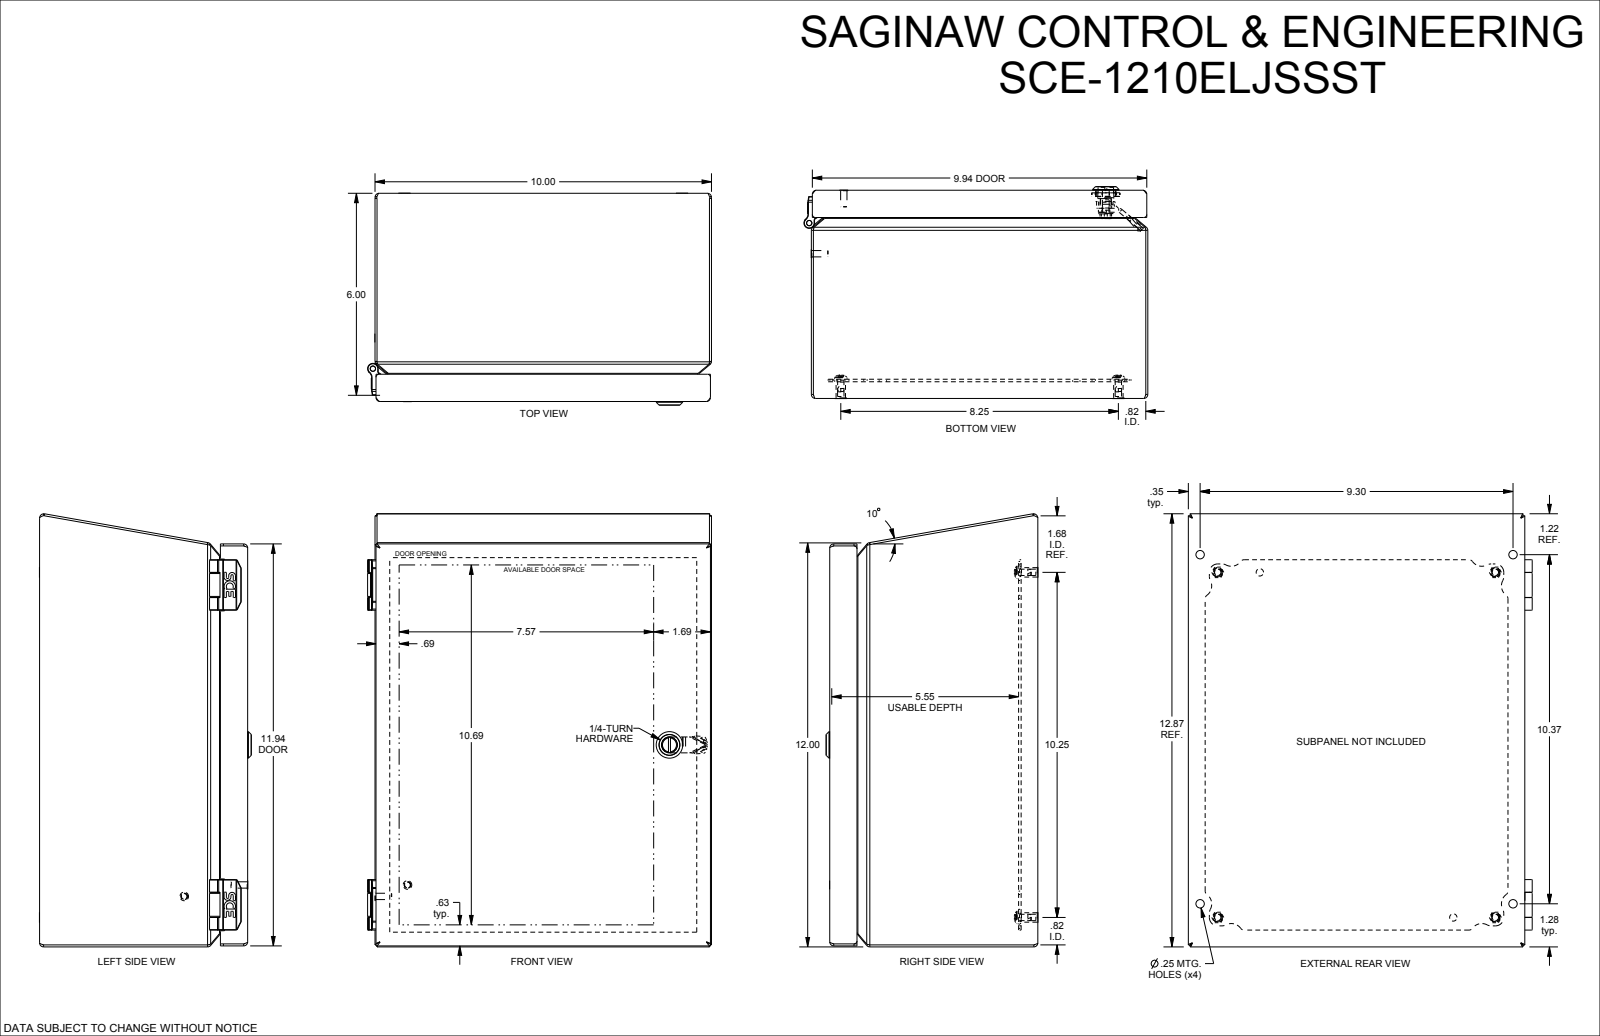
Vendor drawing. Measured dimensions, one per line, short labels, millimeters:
name: SCE-1210ELJSSST
written by: SolidWorks 2021 (AUTOMOTIVE_DESIGN)
unit: mm
bodies: 34 solids, 1454 faces (566 planar, 353 cylindrical, 535 other)
size: 326.7 × 259.6 × 159.9
volume: 712 700 mm³; area: 883 200 mm²
holes: 4× ⌀4.1, 4× ⌀4.8, 4× ⌀6.4, 4× ⌀7.2, 2× ⌀0.5, 2× ⌀2.5, 2× ⌀5.5, 2× ⌀6.8, 1× ⌀4, 1× ⌀5, 1× ⌀5.1, 1× ⌀6.1
bosses: 6× ⌀4.8, 4× ⌀12.3, 4× ⌀9.5, 4× ⌀7.1, 4× ⌀6, 4× ⌀4.1, 2× ⌀6.6, 2× ⌀6.5
rounds: 50× R0.8, 24× R0.2, 21× R0.3, 13× R6.4, 11× R3.2, 10× R0.3, 10× R1.5, 8× R8.7
face distances: 1.5, 1.5, 252.5, 157.1, 155.6, 155.6, 154.1, 14.5, 13, 141.1
hole spacings: 241.3, 0.5, 16.8, 18.9, 31.8, 130.5, 177.8, 209.6
